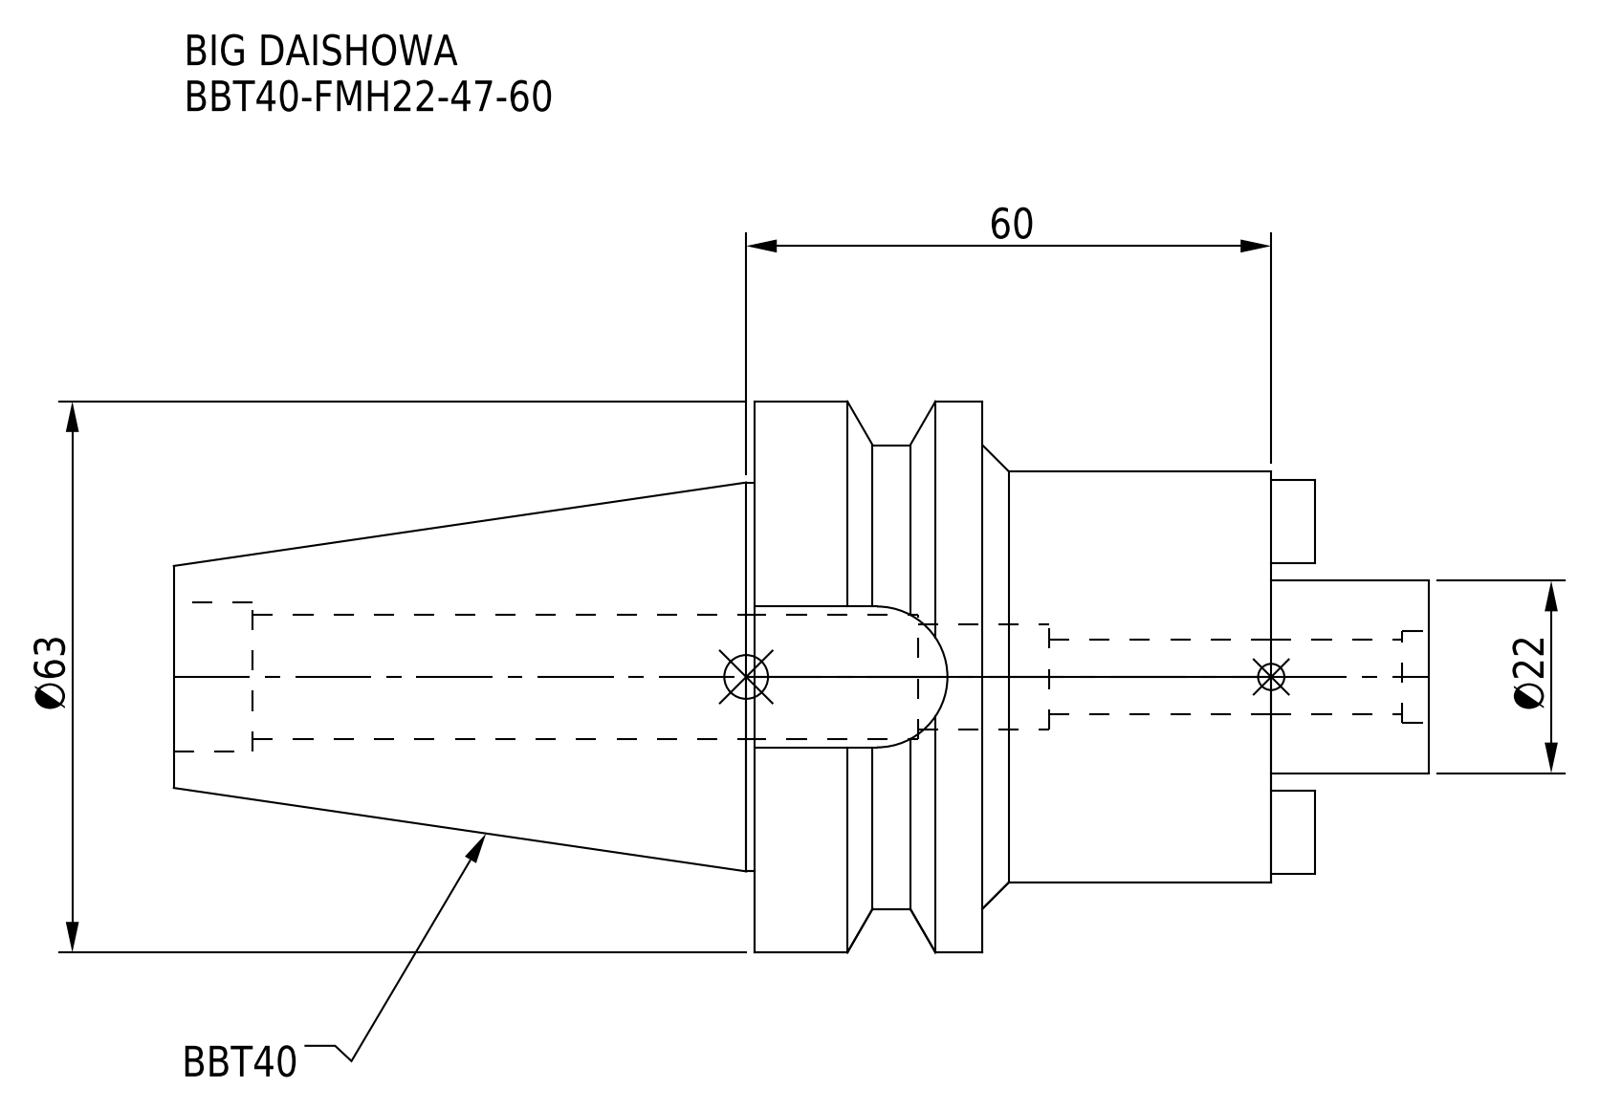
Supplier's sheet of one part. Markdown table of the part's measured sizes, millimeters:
| quantity | value |
| --- | --- |
| part name | BBT40-FMH22-47-60 |
| STEP written by | CREO PARAMETRIC BY PTC INC, 2016380 (AUTOMOTIVE_DESIGN) |
| units | millimeters |
| bodies | 1 solid, 61 faces (25 planar, 28 cylindrical, 8 other) |
| overall size | 143.4 × 63 × 63 |
| volume | 182 990 mm³ |
| surface area | 30 572 mm² |
| round holes (diameter × count) | 8.5 × 1, 10.5 × 1, 12 × 1, 14.2 × 1, 17 × 1 |
| round bosses / shafts (diameter × count) | 63 × 1, 53 × 1, 47 × 1, 44.45 × 1, 22 × 1 |
| partial cylindrical surfaces (radius × count) | 8.05 × 1 |
| main face-to-face distances | 59, 26, 33, 45, 18, 51, 77, 143.4, 125.4, 92.4 |
